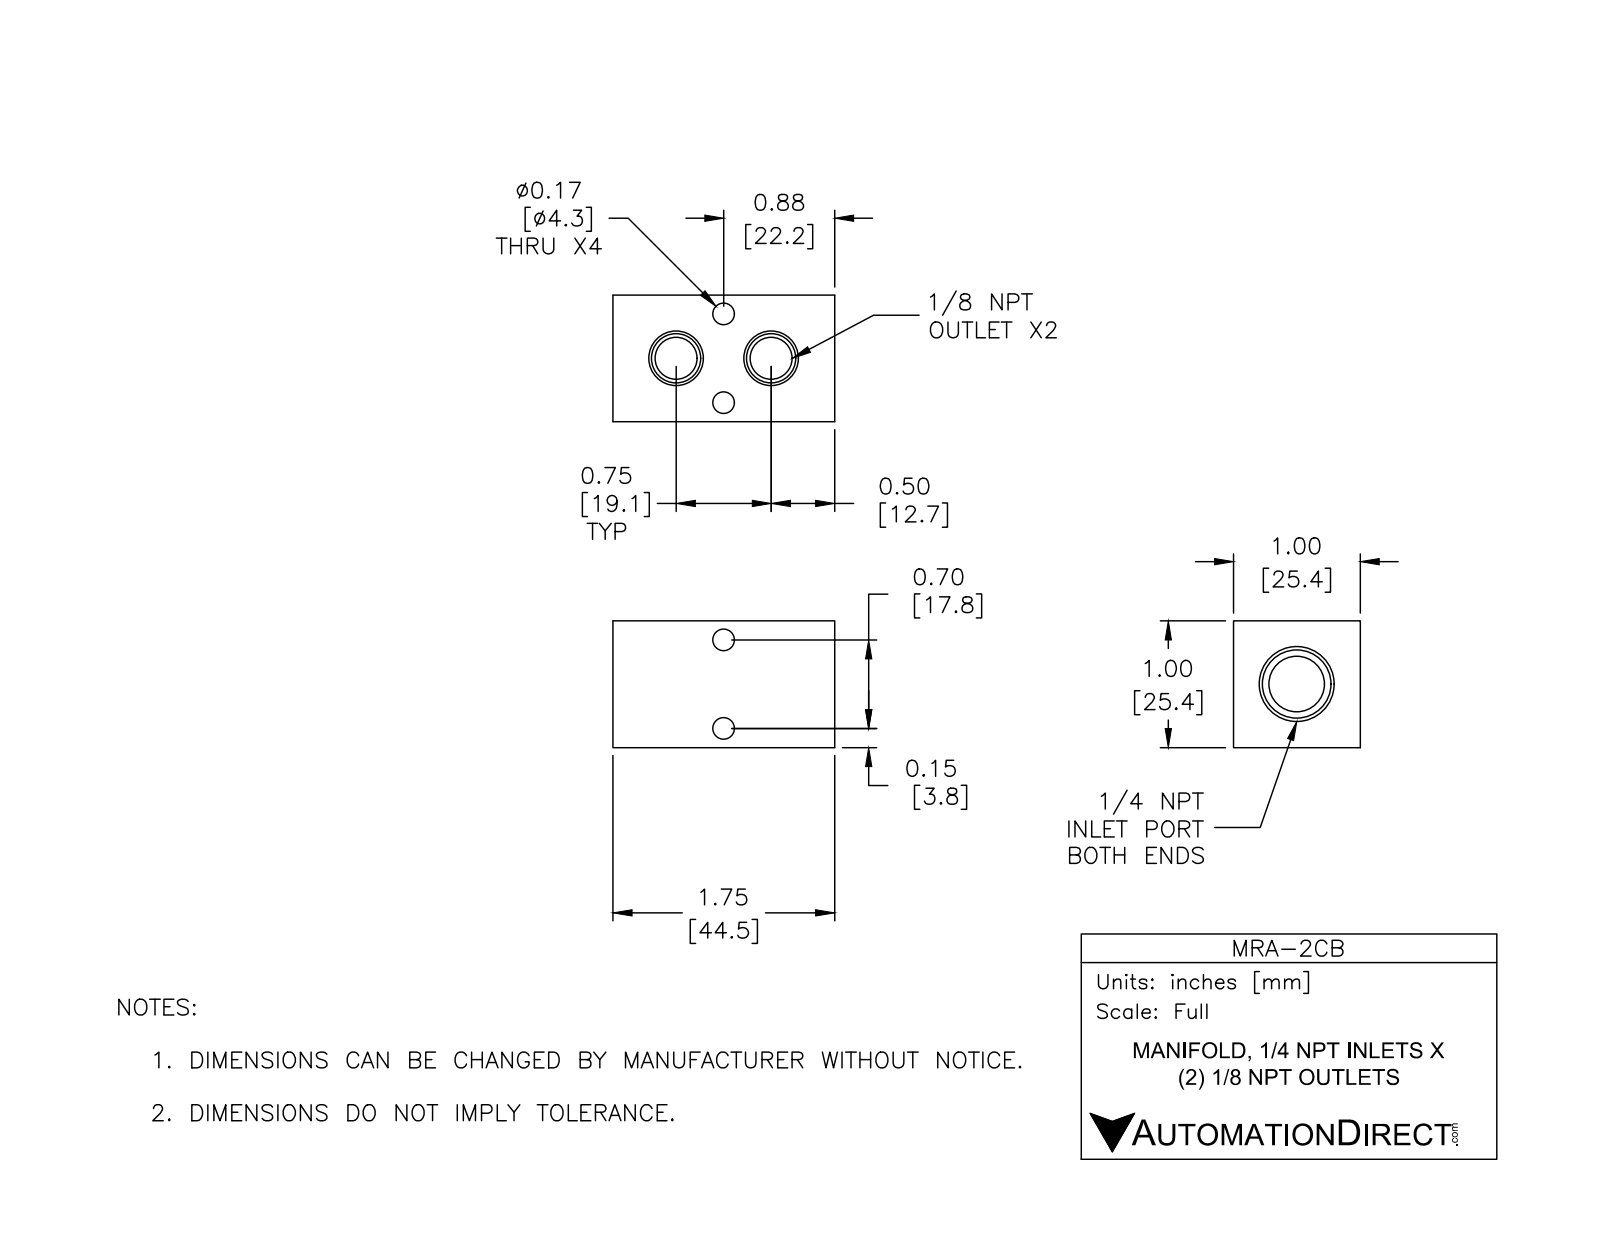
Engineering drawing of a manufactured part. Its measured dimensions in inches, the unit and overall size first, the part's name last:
Units: inches
Overall size (bounding box): 1.75 × 1 × 1
Round holes (diameter × count): ⌀0.17 ×4, ⌀0.438 ×1
Partial cylindrical surfaces — rounded edges, fillets, slot ends (radius × count): R0.166 ×2
Main face-to-face distances: 1, 1.75, 0.39, 1.36, 0.73, 0.27, 0.97
Hole centre spacings: 0.7
Volume: 1.282 in³ · Surface area: 13.04 in²
Bodies: 1 solid, 55 faces (10 planar, 29 cylindrical, 16 other)
Part name (STEP PRODUCT): MRA-2CB
STEP written by: SolidWorks 2015 (CONFIG_CONTROL_DESIGN)
